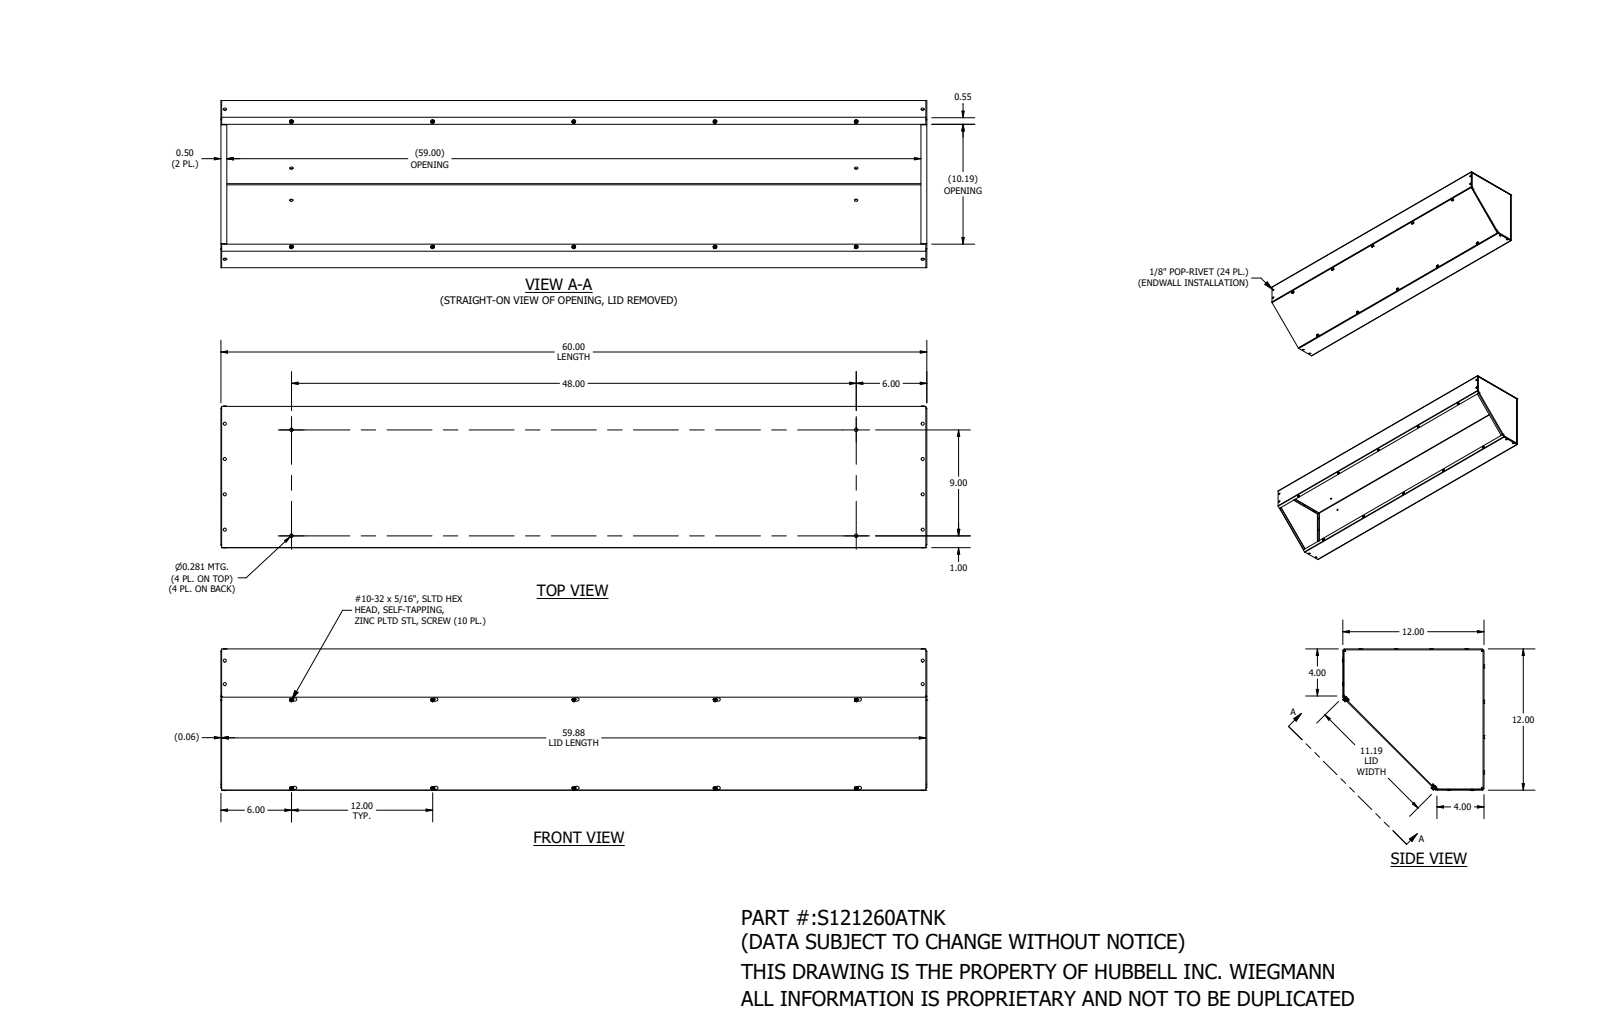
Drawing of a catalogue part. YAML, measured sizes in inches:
part_name: "S121260ATNK"
step_written_by: "SolidWorks 2021 (AUTOMOTIVE_DESIGN)"
units: inches
bodies: {solids: 38, faces: 2104, planar: 470, cylindrical: 574, other: 1060}
overall_size: [60, 12.08, 12.08]
volume: 213
surface_area: 5796
round_holes:
  - {diameter: 0.129, count: 24}
  - {diameter: 0.171, count: 10}
  - {diameter: 0.406, count: 10}
  - {diameter: 0.281, count: 8}
round_bosses_or_shafts:
  - {diameter: 0.262, count: 24}
  - {diameter: 0.125, count: 18}
  - {diameter: 0.313, count: 10}
  - {diameter: 0.181, count: 10}
  - {diameter: 0.125, count: 6}
partial_cylinders:
  - {radius: 0.064, count: 48}
  - {radius: 0.136, count: 15}
  - {radius: 0.109, count: 10}
  - {radius: 0.062, count: 9}
  - {radius: 0.063, count: 6}
face_to_face_distances: [0.074, 11.926, 11.852, 12, 59.926, 0.067, 60, 59.852, 0.141, 0.148]
hole_center_spacings: [12, 3, 24, 59.313, 59.389, 1.5, 5.68, 6]
